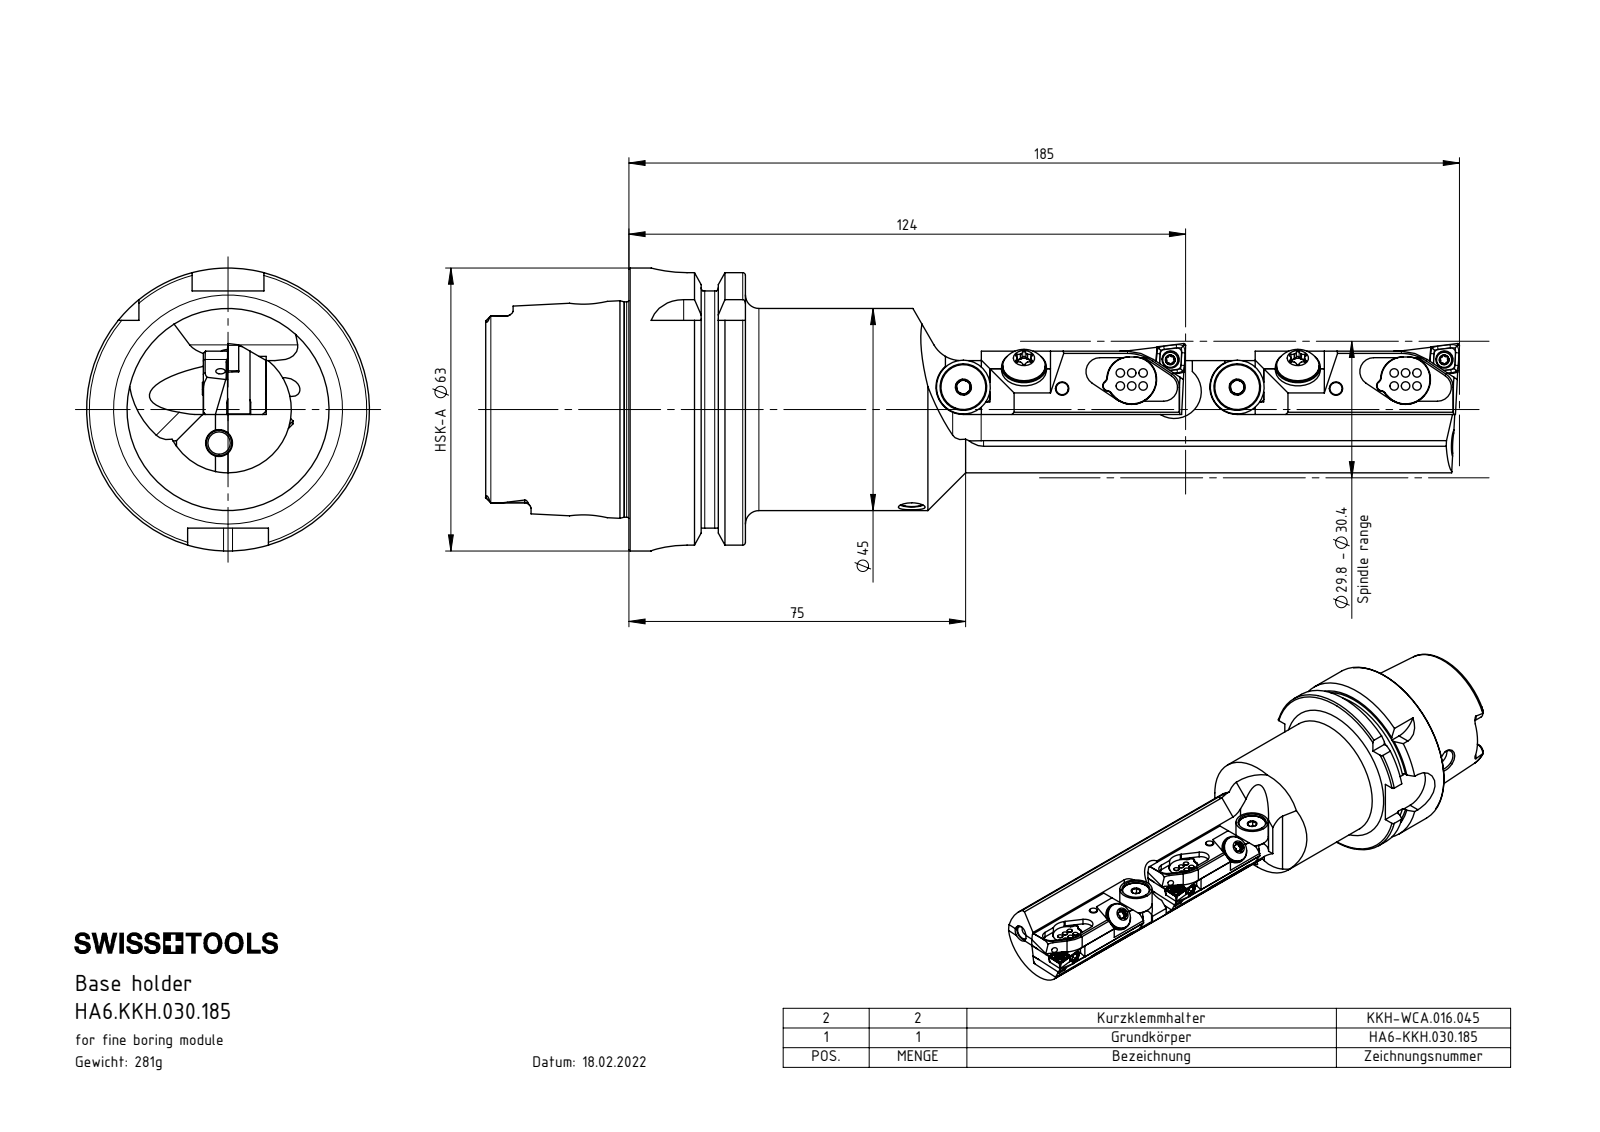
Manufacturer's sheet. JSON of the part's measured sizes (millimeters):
{"part_name": "KKH-WCA.016.045; ISO 7089 - 5_PreviewCfg; HA6.KKH.030.185; ISO 8734 - 3 x 14m6 (+8 more)", "step_written_by": "SolidWorks 2017 (AUTOMOTIVE_DESIGN)", "units": "millimeters", "bodies": {"solids": 33, "faces": 1069, "planar": 581, "cylindrical": 298, "other": 190}, "overall_size": [216.9, 63, 63], "volume_mm3": 194663, "surface_area_mm2": 57542, "round_holes": [[2.5, 6], [4.2, 6], [2.1, 4], [3, 4], [3.3, 4], [2.05, 2], [2.8, 2], [3.65, 2], [3.85, 2], [5, 2], [5.3, 2], [5.5, 2]], "round_bosses_or_shafts": [[1.9, 12], [10, 4], [5, 4], [12, 2], [9.5, 2], [6, 2], [4, 2], [3.4, 2]], "partial_cylinders_radius": [[1.6, 26], [1, 16], [0.21, 12], [0.3, 12], [0.36, 8], [1.1, 8], [1.2, 6], [1.4, 6]], "face_to_face_distances": [3.6, 8.6, 5, 25.95, 5.4, 2.8, 3.2, 9.95, 16, 11.3], "hole_center_spacings": [61, 15.6, 21.6, 22, 23, 23.01, 25.01, 38]}
